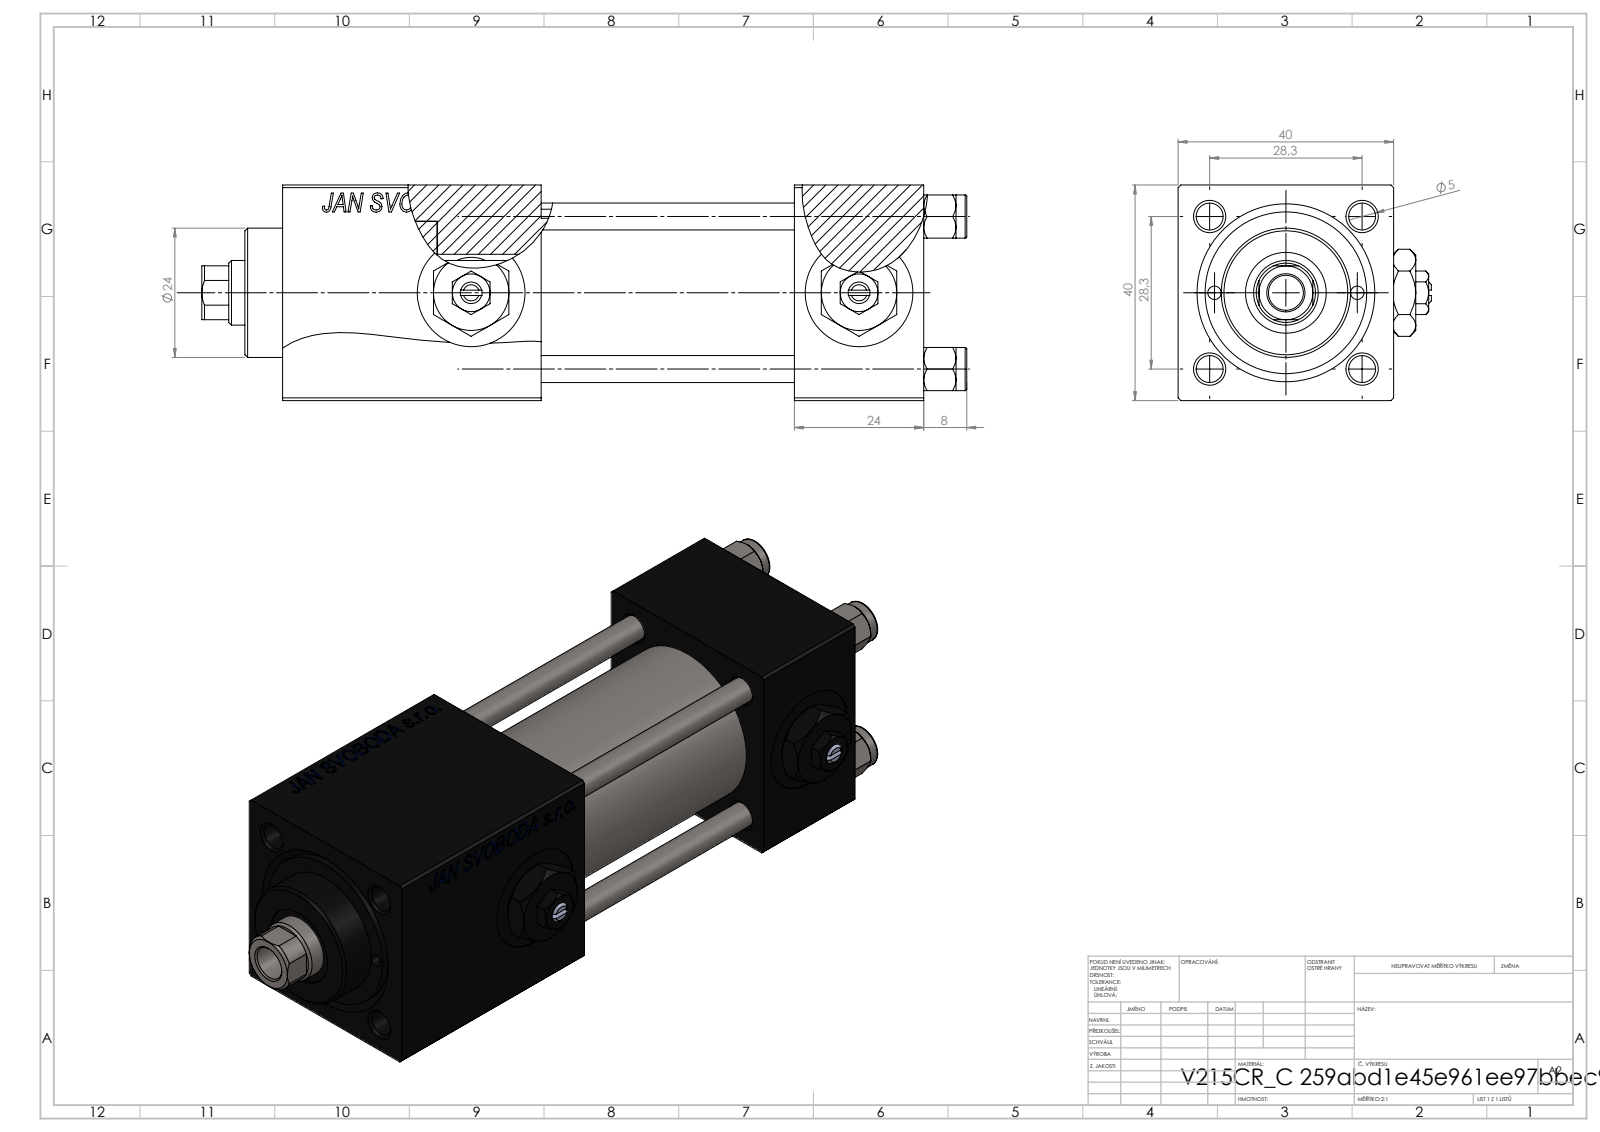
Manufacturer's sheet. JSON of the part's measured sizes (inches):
{"part_name": "Zatka_pro_OIL_PORT; NUT_M5_C; V215CR_C_TYCINKA; V215CR_C_Body (+2 more)", "step_written_by": "SolidWorks 2019 (CONFIG_CONTROL_DESIGN)", "units": "inches", "bodies": {"solids": 13, "faces": 1254, "planar": 574, "cylindrical": 102, "other": 578}, "overall_size": [5.591, 1.85, 1.575], "volume_in3": 8.6, "surface_area_in2": 87.25, "round_holes": [[0.197, 4], [0.787, 3], [0.098, 2], [0.276, 2], [0.518, 2], [0.256, 1], [0.472, 1], [0.591, 1], [0.984, 1], [1.181, 1]], "round_bosses_or_shafts": [[0.315, 4], [1.22, 1], [0.945, 1]], "partial_cylinders_radius": [[0.217, 1]], "face_to_face_distances": [1.575, 0.945, 1.567, 3.555, 2.61, 1.85, 1.89, 2.795, 0.76, 3.74], "hole_center_spacings": [0.558, 0.788, 1.114, 1.214, 0.522, 1.576, 1.043, 2.835]}
